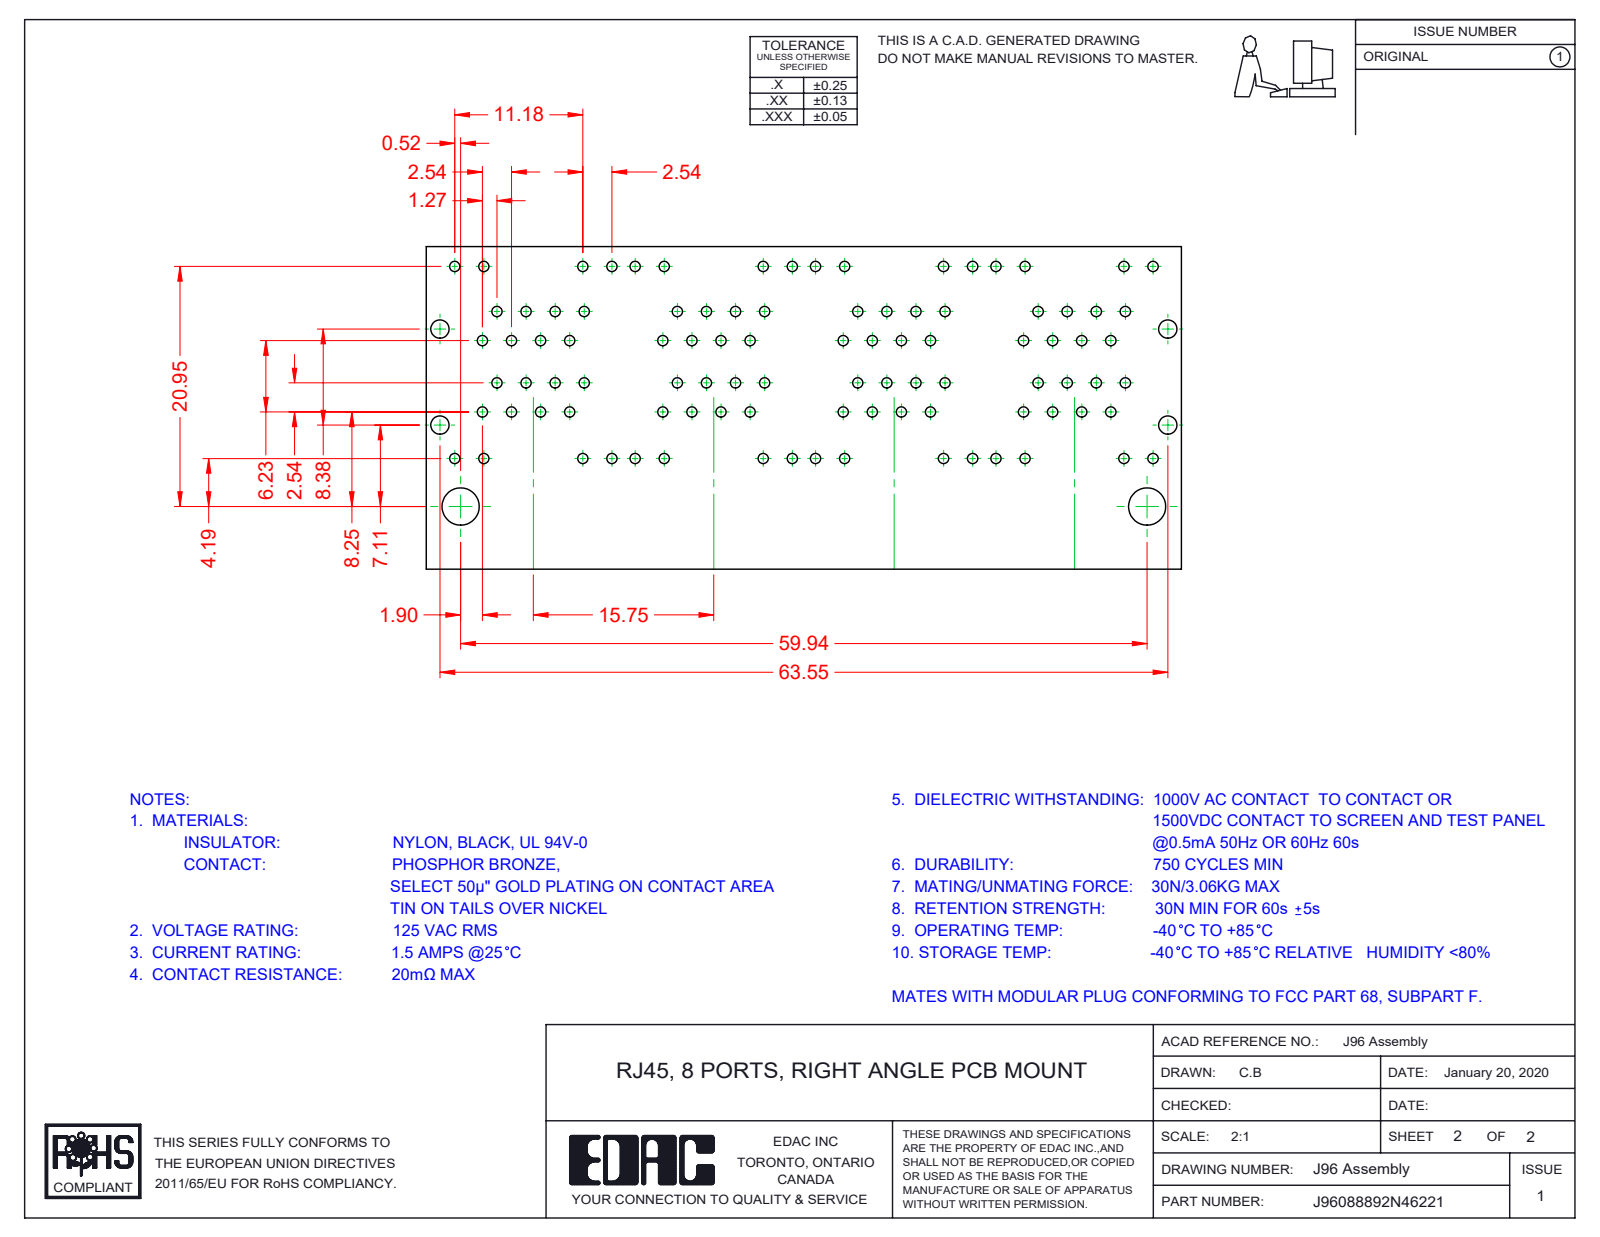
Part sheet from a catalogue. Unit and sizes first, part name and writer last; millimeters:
Units: millimetres
Overall size (bounding box): 67.35 × 31.38 × 28.68
Round holes (diameter × count): ⌀1.7 ×3
Round bosses / shafts (diameter × count): ⌀1.68 ×3
Partial cylindrical surfaces — rounded edges, fillets, slot ends (radius × count): R0.25 ×124, R0.35 ×73, R1 ×72, R0.5 ×49, R0.91 ×32, R0.2 ×27, R0.27 ×14, R0.7 ×11
Main face-to-face distances: 15.75, 0.35, 9.95, 1.17, 1.6, 0.54, 9.98, 10.18, 12.67, 3.37
Hole centre spacings: 15.75, 31.5
Volume: 24 149 mm³ · Surface area: 63 596 mm²
Bodies: 96 solids, 7820 faces (6105 planar, 1404 cylindrical, 311 other)
Part name (STEP PRODUCT): 96 Contact Lock Lower; 96 Contacts Lower; 96 Shield_8 Ports LED - EMI; 96 LED LH Lower_4-Orange (+8 more)
STEP written by: SolidWorks 2016 (CONFIG_CONTROL_DESIGN)
